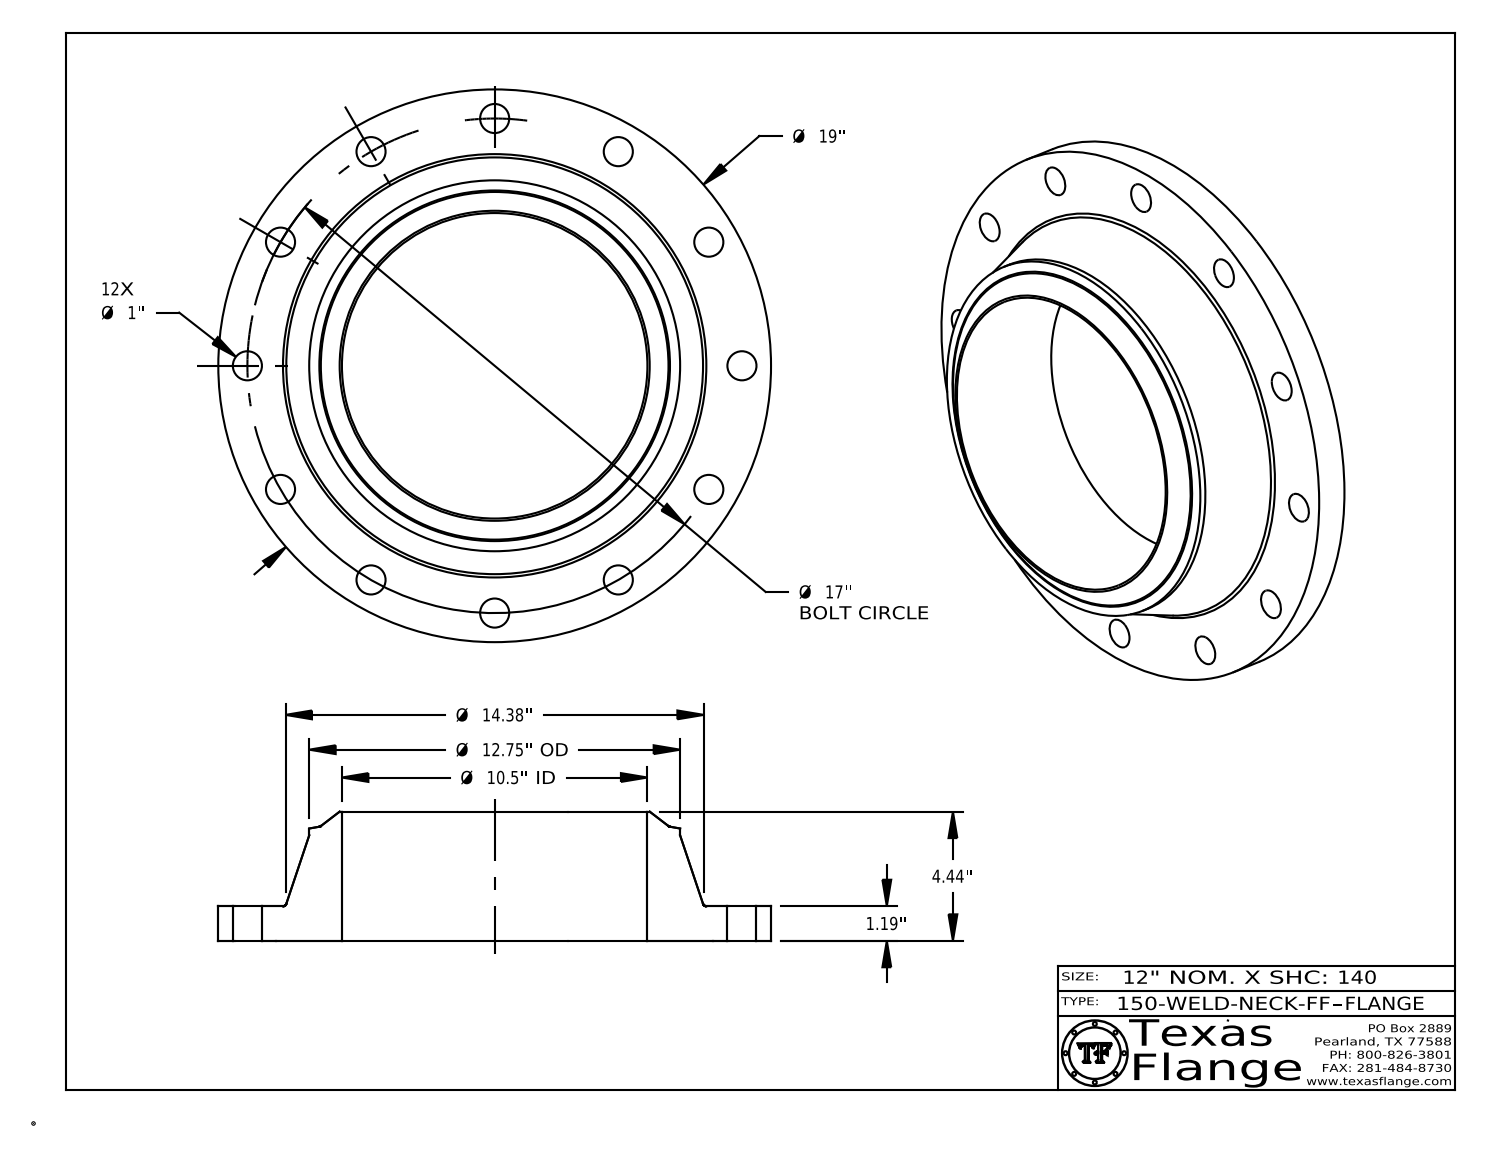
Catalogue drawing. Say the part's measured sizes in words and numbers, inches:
The part is named "150-WELD-NECK-FF". Its 3-D file was written by "CATIA V5 STEP AP214 (AUTOMOTIVE_DESIGN)". It is 1 solid with 429 faces: 369 planar, 50 cylindrical and 10 other. Overall it measures 19 by 19 by 4.44 inches. Its volume is 383.9 cubic inches and its surface area 726.9 square inches. Round holes: 12 of diameter 1, 1 of diameter 0.495, 1 of diameter 10.5. Round bosses or shafts: 8 of diameter 0.03, 1 of diameter 19, 1 of diameter 12.75, 1 of diameter 0.39. The main face-to-face distances are 1.19, 4.44, 3.25, 0.015, 1.175, 3.265, 0.148, 0.145, 0.027, 0.096. The hole center spacings are 8.5, 16.42, 4.4, 12.02, 14.722, 4.4, 12.021, 14.722.
